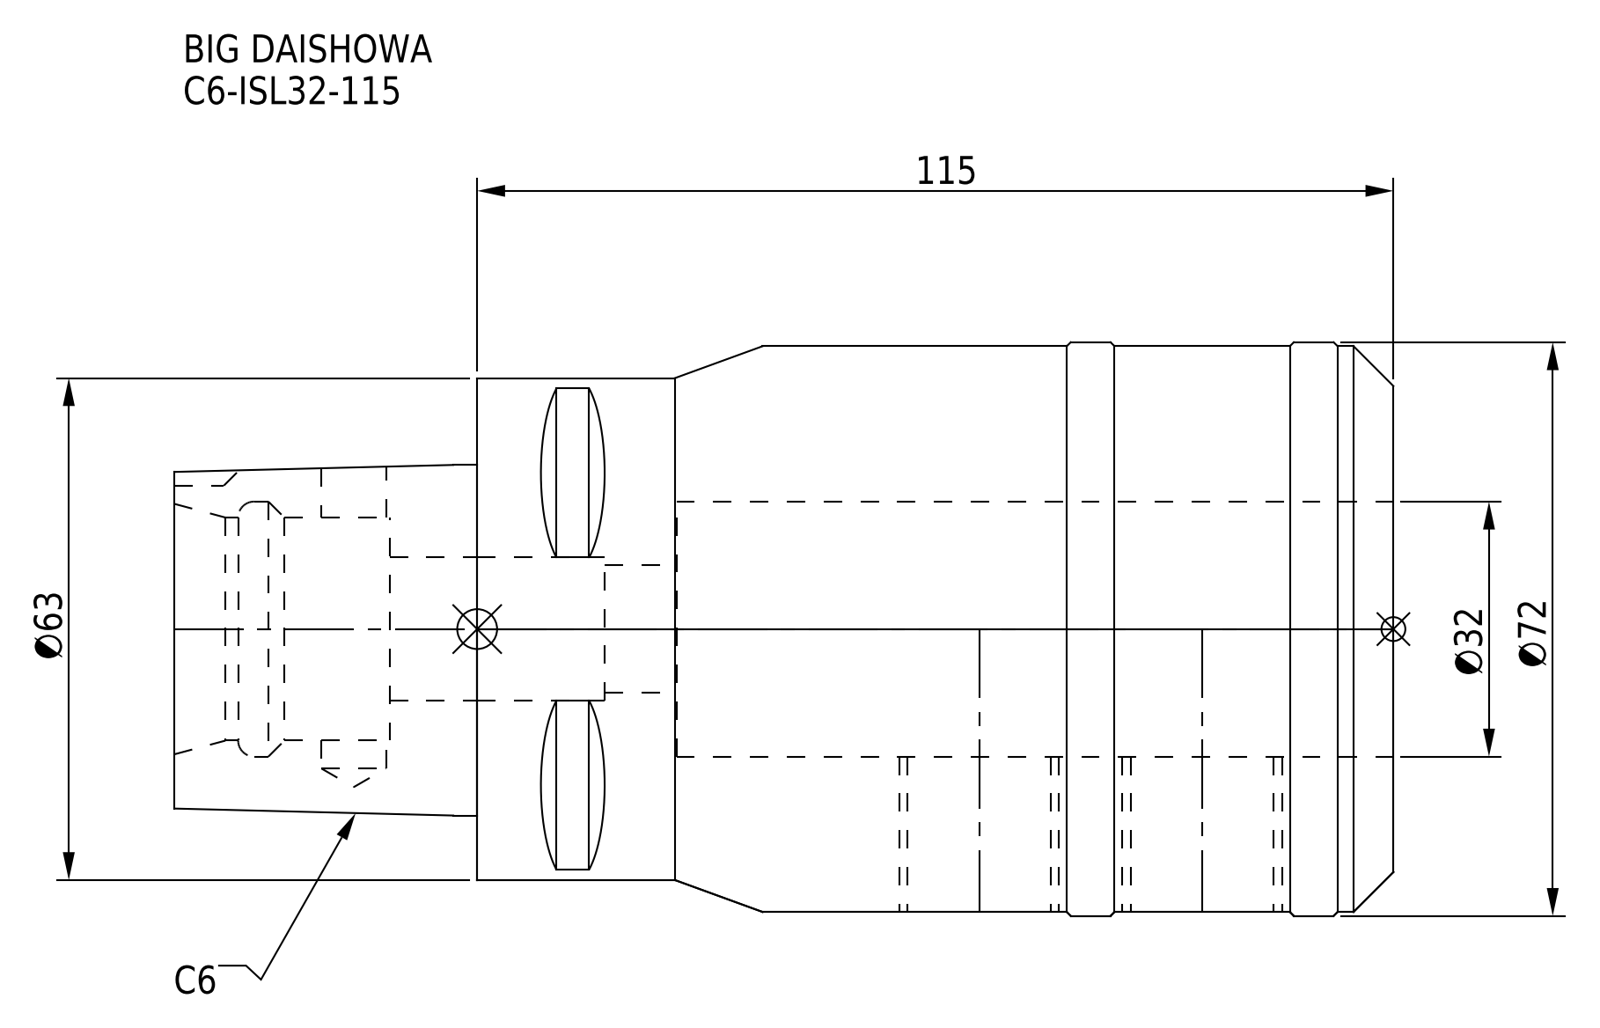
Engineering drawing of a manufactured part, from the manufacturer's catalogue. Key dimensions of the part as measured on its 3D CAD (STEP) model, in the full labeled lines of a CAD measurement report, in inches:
Part name (STEP PRODUCT): C6-ISL32-115
STEP written by: CREO PARAMETRIC BY PTC INC, 2016380 (AUTOMOTIVE_DESIGN)
Units: inches
Bodies: 1 solid, 79 faces (28 planar, 29 cylindrical, 22 other)
Overall size (bounding box): 6.024 × 2.835 × 2.835
Volume: 23.32 in³ · Surface area: 77.98 in²
Round holes (diameter × count): ⌀0.319 ×1, ⌀0.63 ×1, ⌀0.709 ×1, ⌀1.102 ×1, ⌀1.26 ×1
Round bosses / shafts (diameter × count): ⌀2.835 ×1, ⌀2.795 ×1, ⌀2.48 ×1
Partial cylindrical surfaces — rounded edges, fillets, slot ends (radius × count): R0.197 ×1
Main face-to-face distances: 4.528, 3.543, 0.984, 6.024, 2.48, 1.496, 1.063, 4.961, 1.417, 0.433
